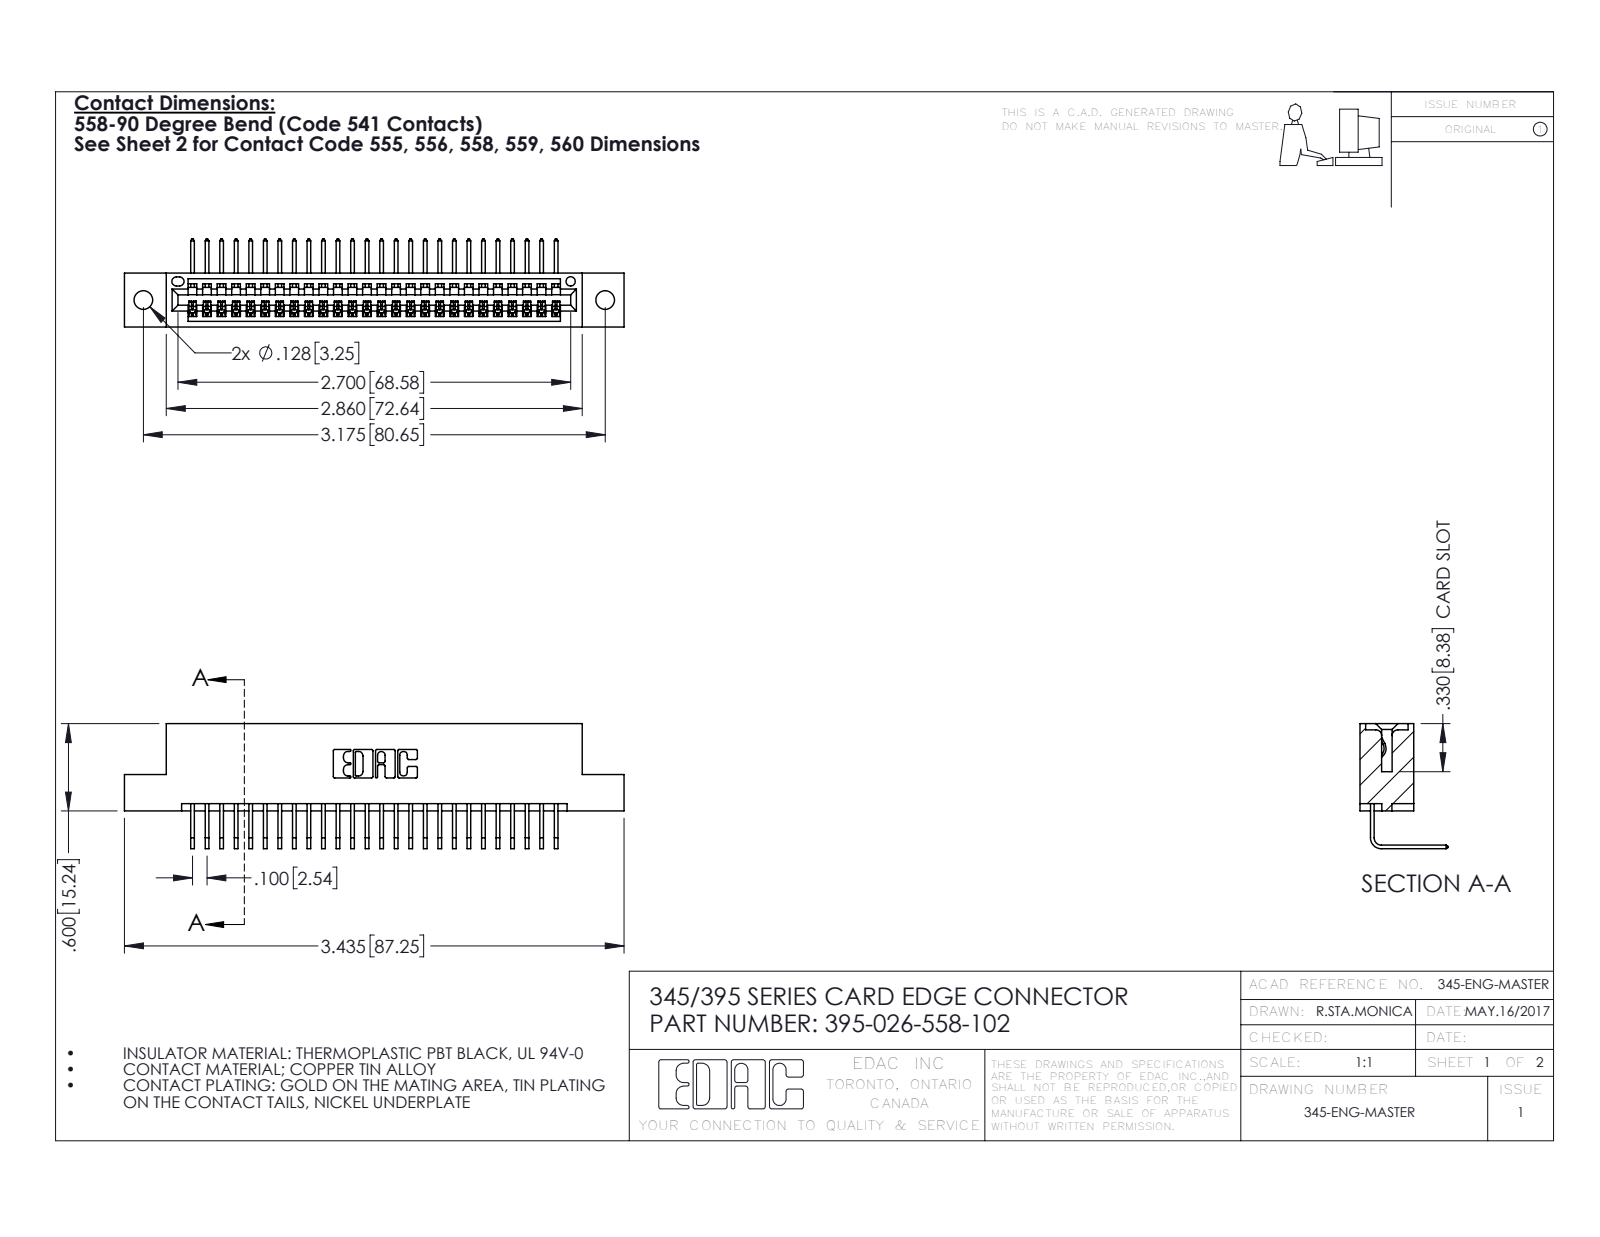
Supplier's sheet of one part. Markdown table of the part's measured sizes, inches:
| quantity | value |
| --- | --- |
| part name | 345-292-001_558 Tail - 2; 395-026-558-102; 345 Part_Flush Mounting Lugs - 0.128 Dia |
| STEP written by | SolidWorks 2016 (CONFIG_CONTROL_DESIGN) |
| units | inches |
| bodies | 27 solids, 1686 faces (1172 planar, 514 cylindrical, 0 other) |
| overall size | 3.435 × 0.859 × 0.605 |
| volume | 0.501 in³ |
| surface area | 16.93 in² |
| round holes (diameter × count) | 0.128 × 2, 0.064 × 1 |
| partial cylindrical surfaces (radius × count) | 0.006 × 52, 0.01 × 22, 0.007 × 6, 0.031 × 6, 0.026 × 3, 0.031 × 2, 0.04 × 2, 0.014 × 1 |
| main face-to-face distances | 0.298, 0.072, 0.2, 0.37, 0.098, 0.272, 0.025, 0.225, 0.149, 0.072 |
| hole center spacings | 0.27, 2.94, 3.175 |
